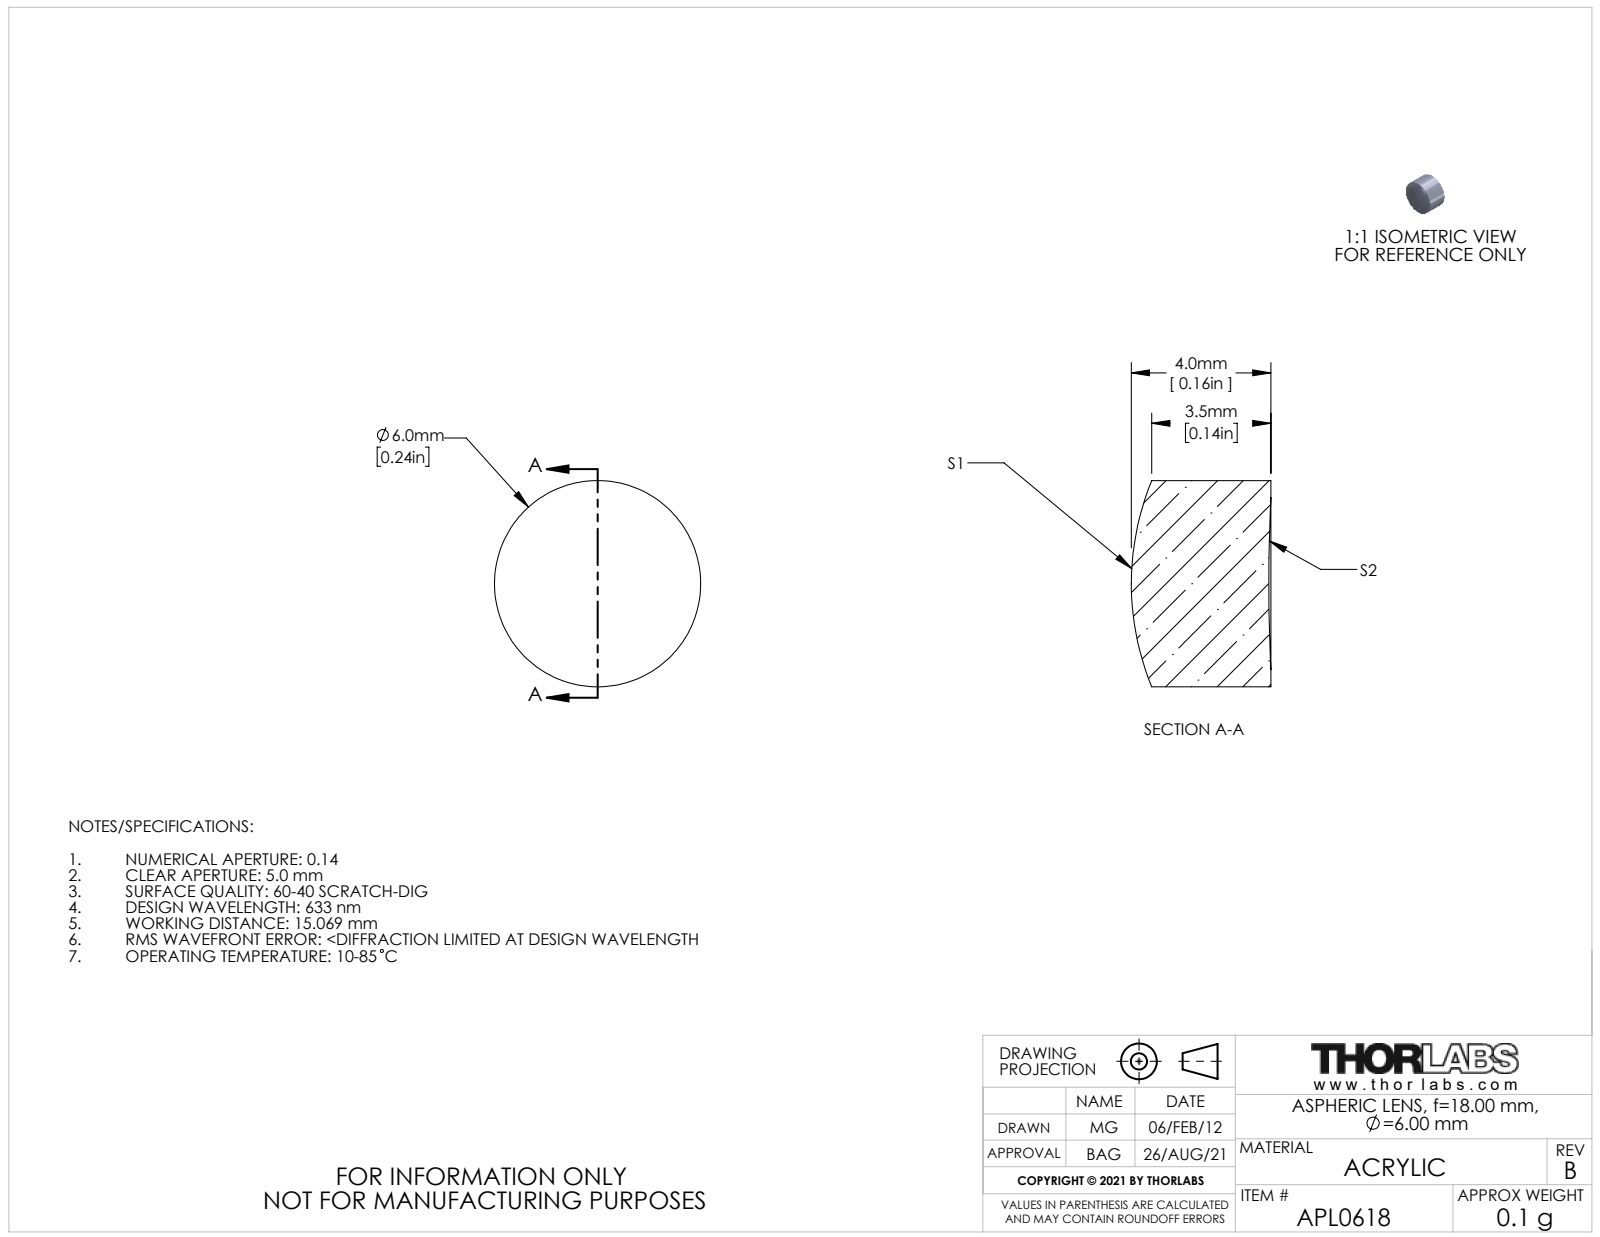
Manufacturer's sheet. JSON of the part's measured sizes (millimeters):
{"part_name": "23430-E0W", "step_written_by": "SolidWorks 2011 (AUTOMOTIVE_DESIGN)", "units": "millimeters", "bodies": {"solids": 1, "faces": 7, "planar": 1, "cylindrical": 2, "other": 4}, "overall_size": [6, 6, 4.06], "volume_mm3": 106, "surface_area_mm2": 123, "round_bosses_or_shafts": [[6, 1]]}
